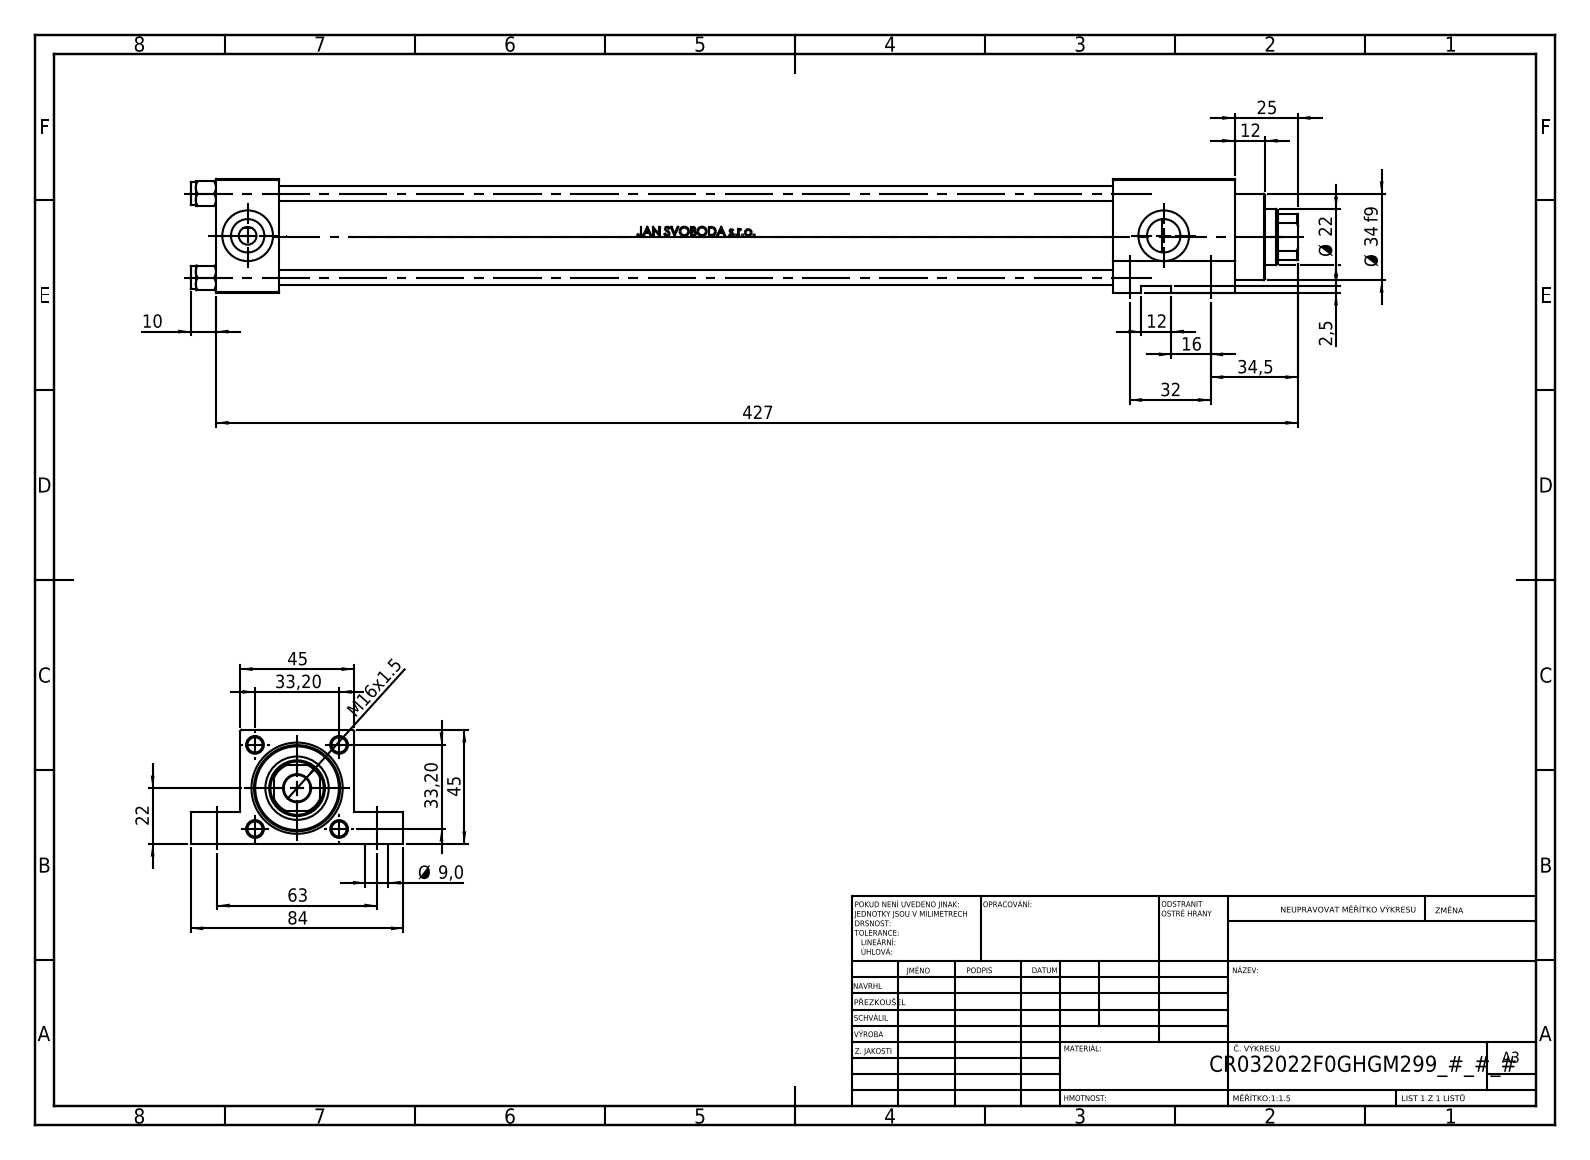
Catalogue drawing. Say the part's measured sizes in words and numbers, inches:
The part is named "V215CR_F_TYCINKA; V215_VC_A; NUT_M5_F; V215CR_F_Body (+1 more)". Its 3-D file was written by "SolidWorks 2019 (CONFIG_CONTROL_DESIGN)". It is 11 solids with 1102 faces: 436 planar, 126 cylindrical and 540 other. Overall it measures 17.205 by 3.307 by 1.772 inches. Its volume is 27.94 cubic inches and its surface area 276.6 square inches. Round holes: 4 of diameter 0.236, 4 of diameter 0.354, 2 of diameter 0.276, 2 of diameter 0.518, 2 of diameter 0.787, 1 of diameter 0.413, 1 of diameter 0.866, 1 of diameter 0.945, 1 of diameter 0.984, 1 of diameter 1.26, 1 of diameter 1.299. Round bosses or shafts: 4 of diameter 0.354, 1 of diameter 1.496, 1 of diameter 1.339. Partial cylindrical surfaces (rounded edges, fillets, slot ends): 1 of radius 0.413. The main face-to-face distances are 1.772, 0.984, 14.843, 15.827, 13.937, 12.953, 0.492, 1.28, 1.89, 0.394. The hole center spacings are 1.307, 0.911, 0.938, 1.26, 1.848, 2.48, 2.782, 14.232.
